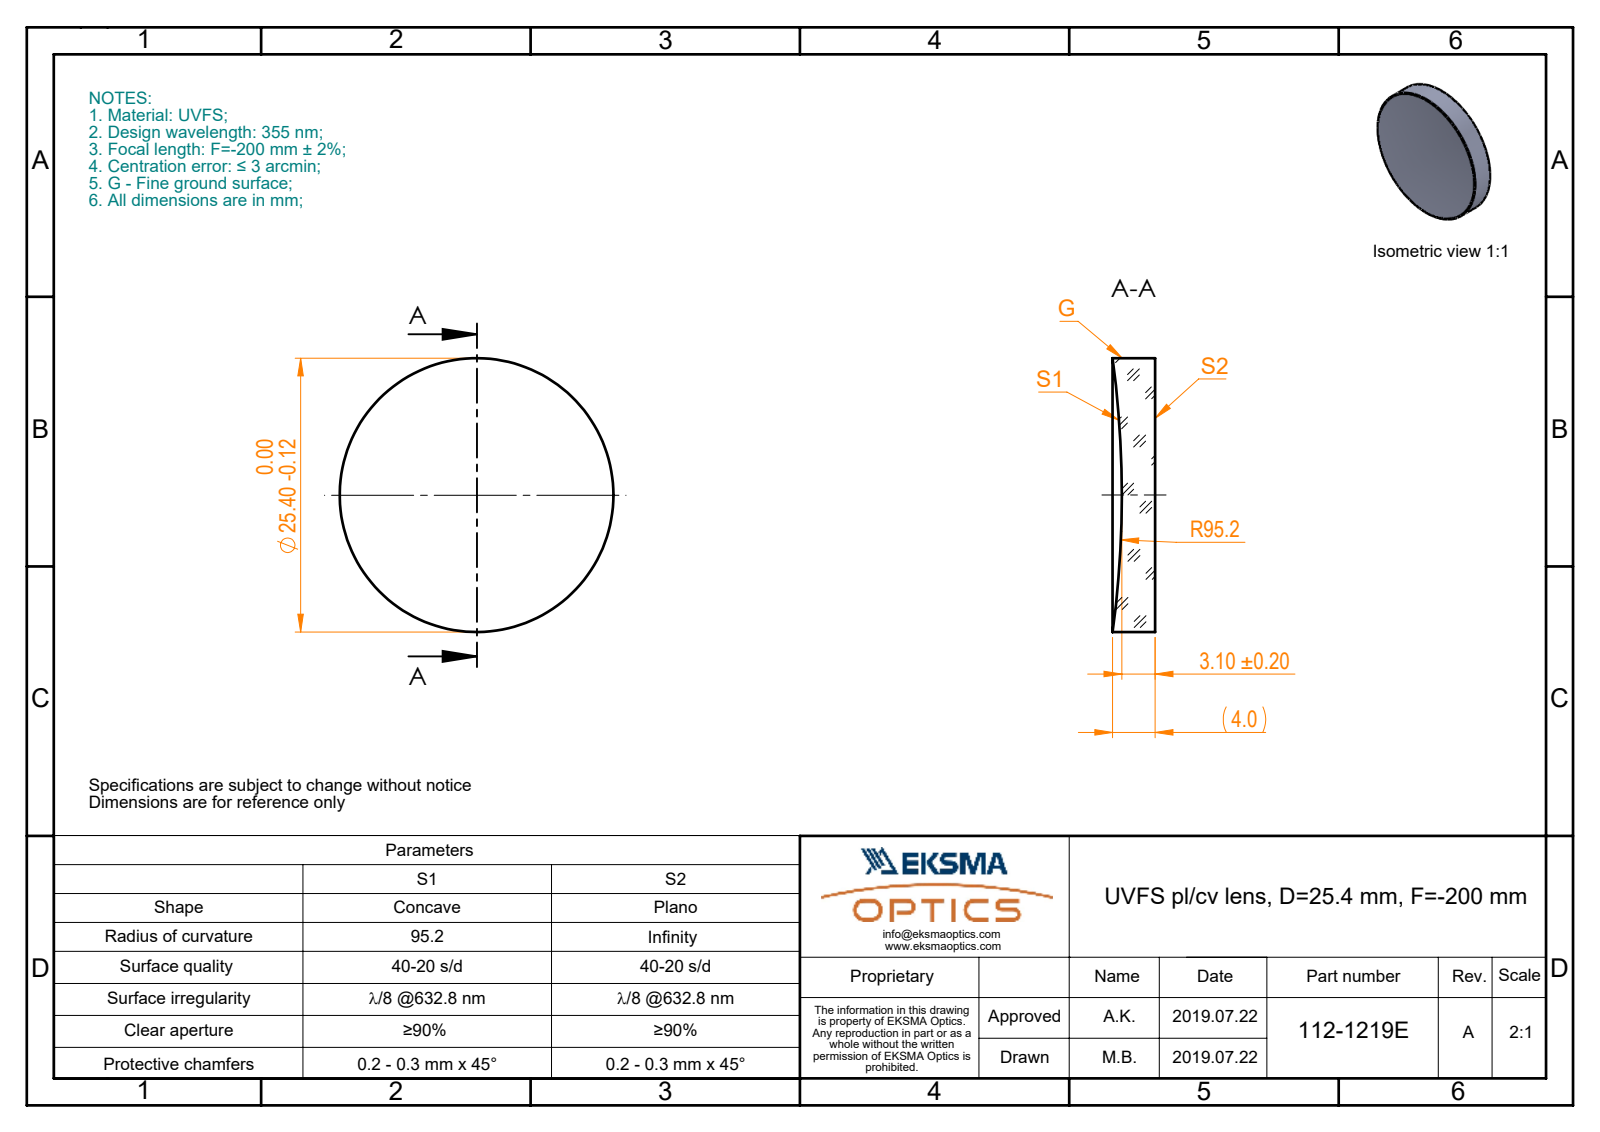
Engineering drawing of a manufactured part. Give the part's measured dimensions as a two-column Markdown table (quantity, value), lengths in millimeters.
| quantity | value |
| --- | --- |
| part name | 112-1219E UVFS pl-cv 25.4 F-200 |
| STEP written by | SolidWorks 2017 (CONFIG_CONTROL_DESIGN) |
| units | millimeters |
| bodies | 1 solid, 5 faces (1 planar, 2 cylindrical, 2 other) |
| overall size | 25.4 × 25.4 × 3.95 |
| volume | 1 786 mm³ |
| surface area | 1 331 mm² |
| round bosses / shafts (diameter × count) | 25.4 × 1 |
